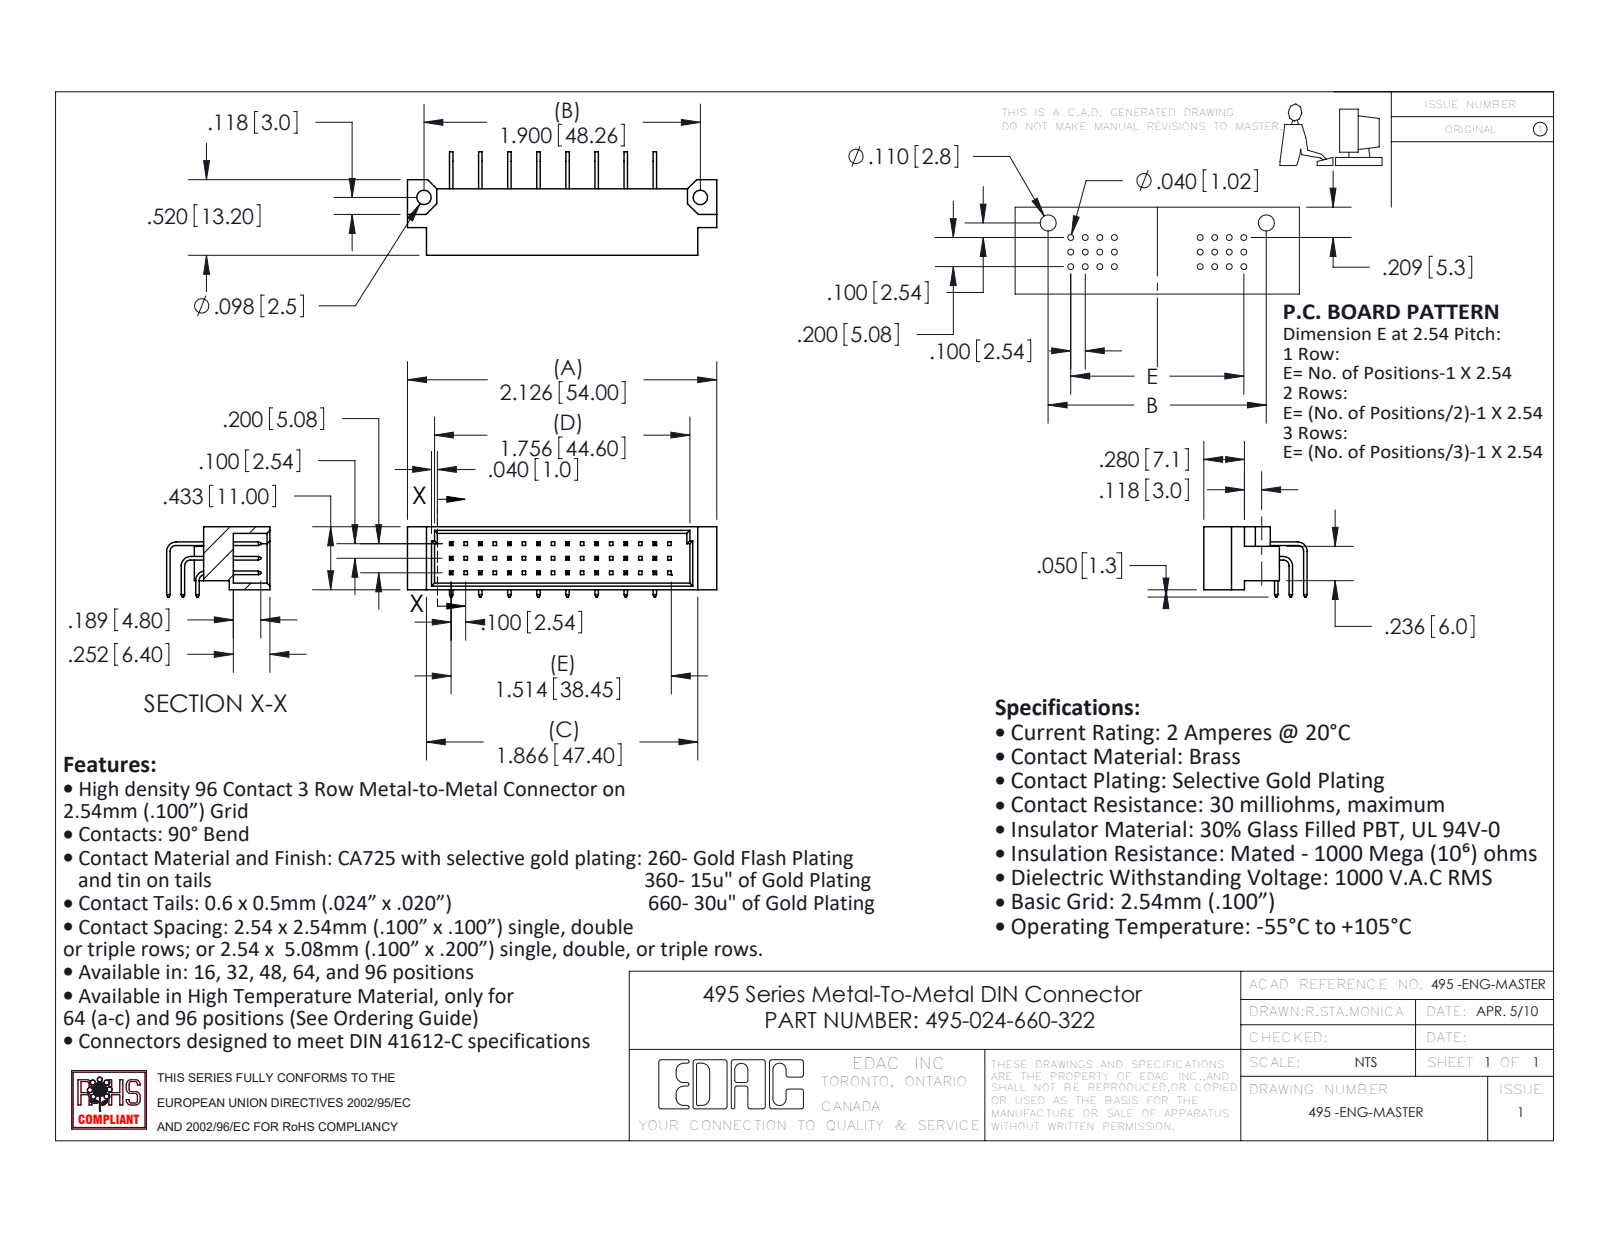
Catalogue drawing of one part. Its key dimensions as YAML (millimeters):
part_name: "495-290-2; 495-024-660-322; 495-290-3; 495 Part_48 (+1 more)"
step_written_by: "SolidWorks 2020 (AUTOMOTIVE_DESIGN)"
units: millimeters
bodies: {solids: 25, faces: 674, planar: 622, cylindrical: 52, other: 0}
overall_size: [54, 18.05, 12.27]
volume: 3622
surface_area: 5113
round_holes:
  - {diameter: 2.49, count: 2}
partial_cylinders:
  - {radius: 1.02, count: 3}
  - {radius: 1.65, count: 3}
face_to_face_distances: [5.08, 10.16, 1.14, 9.86, 2.54, 5.2, 15.24, 0.61, 0.6, 20.32]
hole_center_spacings: [48.26]
